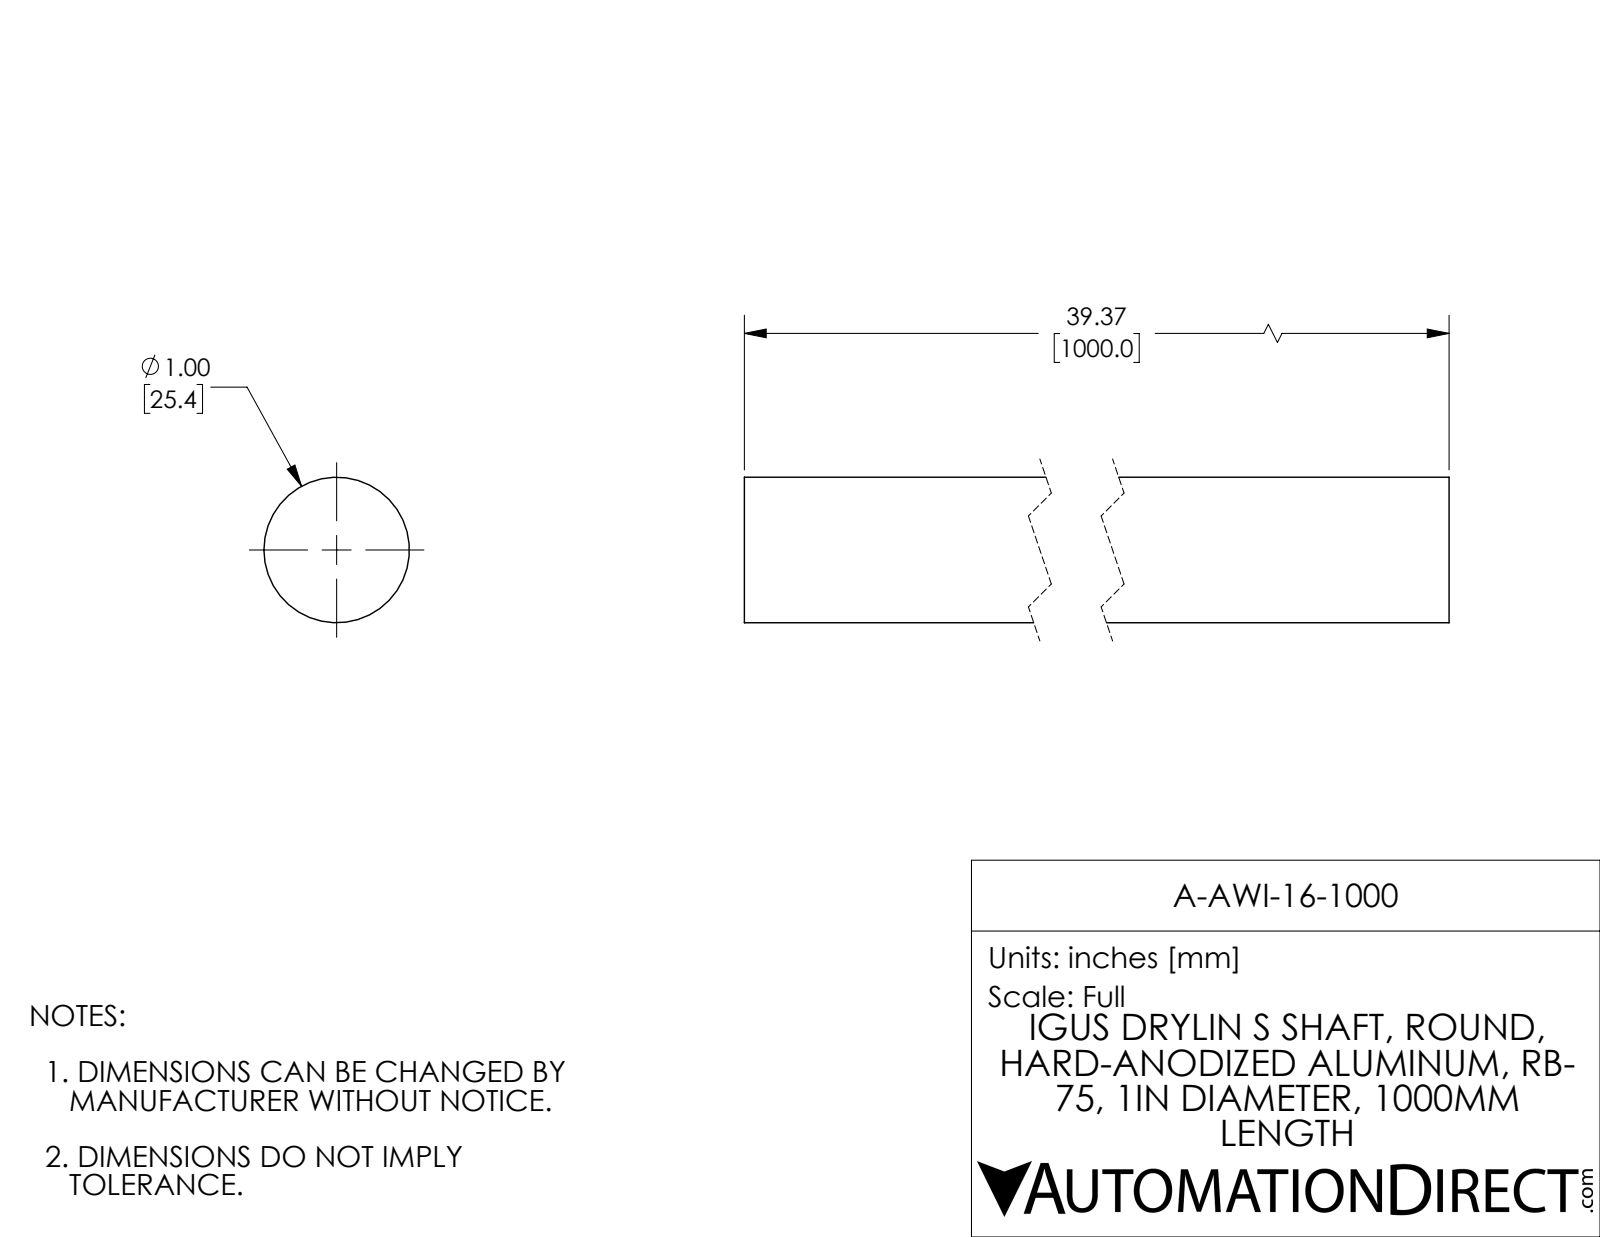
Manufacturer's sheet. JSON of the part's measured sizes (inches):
{"part_name": "A-AWI-16-1000", "step_written_by": "SolidWorks 2017 (AUTOMOTIVE_DESIGN)", "units": "inches", "bodies": {"solids": 1, "faces": 4, "planar": 2, "cylindrical": 2, "other": 0}, "overall_size": [39.37, 1, 1], "volume_in3": 30.92, "surface_area_in2": 125.3, "round_bosses_or_shafts": [[1, 1]], "face_to_face_distances": [39.37]}
